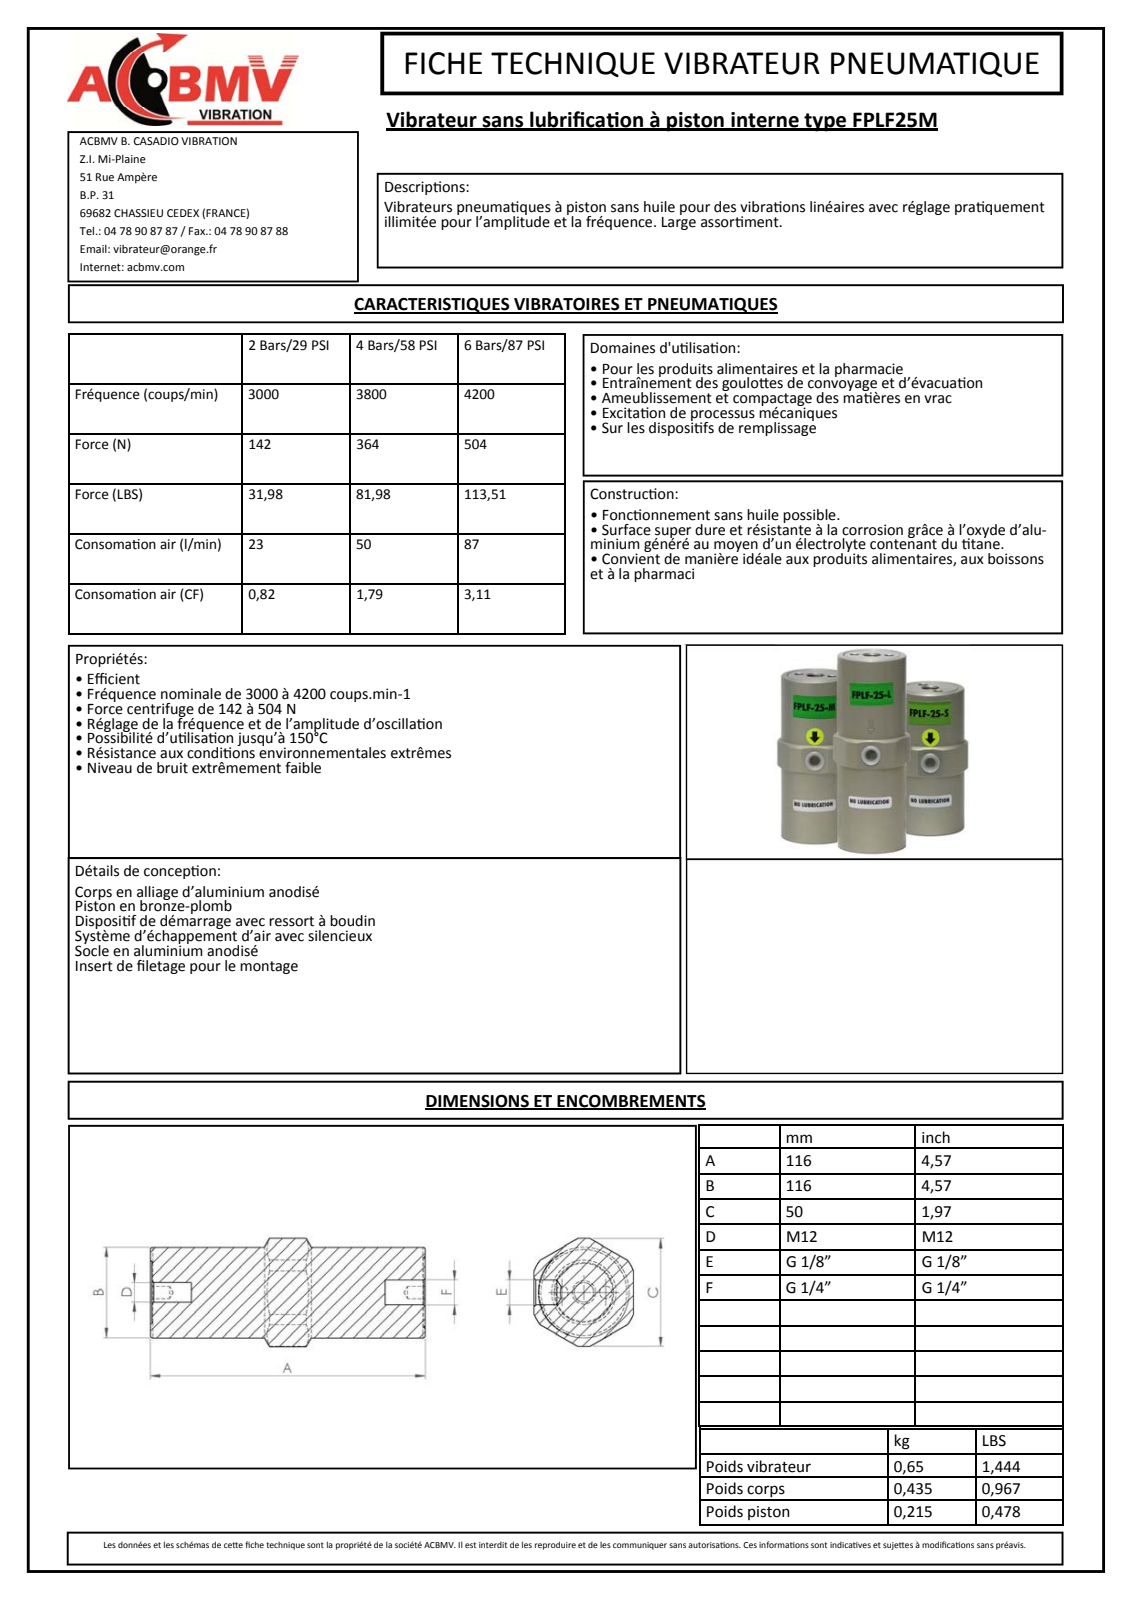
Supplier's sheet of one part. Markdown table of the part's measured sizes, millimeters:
| quantity | value |
| --- | --- |
| part name | 9525-20-M |
| STEP written by | Autodesk Inventor 2011 (CONFIG_CONTROL_DESIGN) |
| units | millimeters |
| bodies | 1 solid, 482 faces (185 planar, 63 cylindrical, 234 other) |
| overall size | 116 × 53.5 × 50 |
| volume | 210 540 mm³ |
| surface area | 23 712 mm² |
| round holes (diameter × count) | 6.2 × 4, 2.5 × 1, 8.57 × 1, 10.11 × 1, 11.45 × 1 |
| round bosses / shafts (diameter × count) | 48 × 1 |
| partial cylindrical surfaces (radius × count) | 14.5 × 1, 23.8 × 1, 24.08 × 1, 24.1 × 1, 26.75 × 1 |
| main face-to-face distances | 50, 116, 0.5, 115.5, 102.3, 101.8, 13.7, 19, 18.5, 83.3 |
| hole center spacings | 1, 11, 12, 23, 22, 24 |
